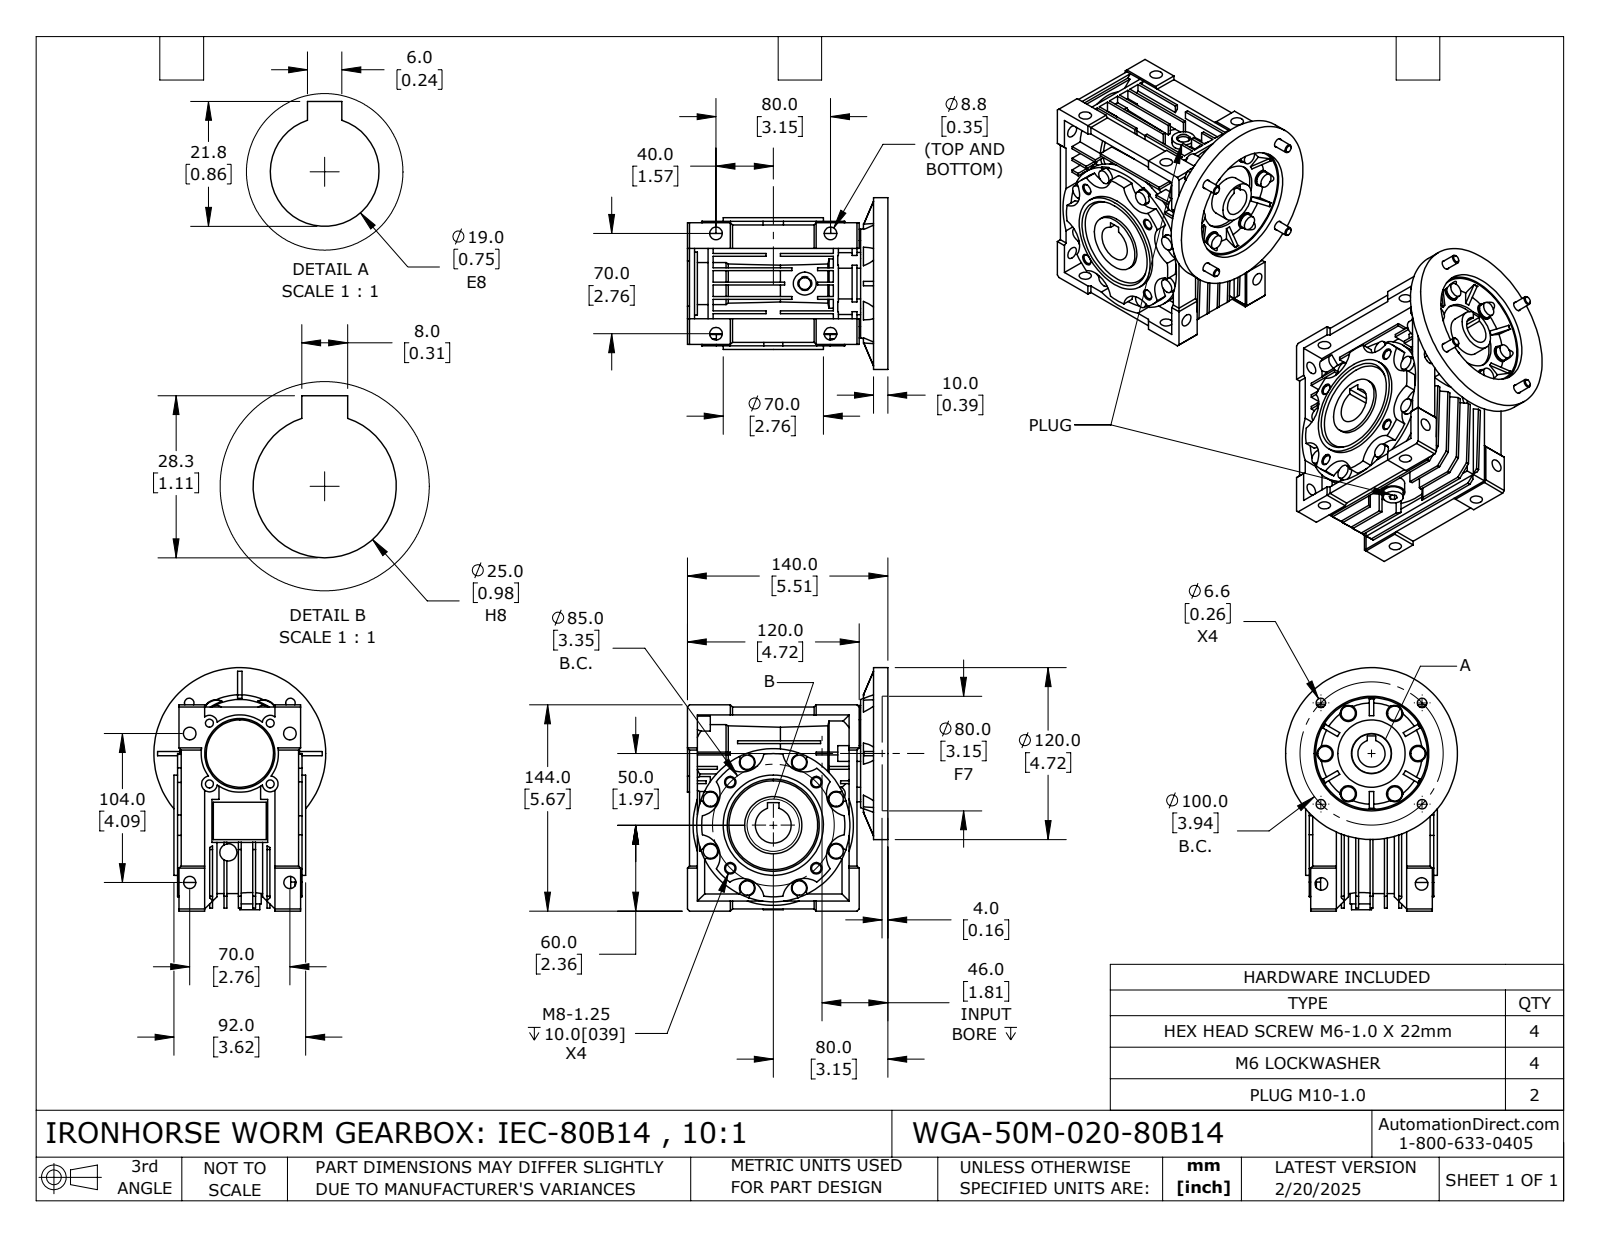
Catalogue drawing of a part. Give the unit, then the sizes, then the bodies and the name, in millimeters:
Units: millimetres
Overall size (bounding box): 170 × 150.5 × 120
Round holes (diameter × count): ⌀8.8 ×8, ⌀8.5 ×6, ⌀5.55 ×4, ⌀6.1 ×4, ⌀6.6 ×4, ⌀6.65 ×2, ⌀6.65 ×2, ⌀9 ×2, ⌀19 ×1, ⌀20 ×1, ⌀25 ×1, ⌀28 ×1
Round bosses / shafts (diameter × count): ⌀10 ×14, ⌀12.2 ×4, ⌀6 ×4, ⌀16 ×2, ⌀120 ×1, ⌀107 ×1, ⌀70 ×1, ⌀61 ×1
Partial cylindrical surfaces — rounded edges, fillets, slot ends (radius × count): R5.5 ×18, R6 ×8, R15 ×8, R15.5 ×8, R5.75 ×6, R20.76 ×1, R46 ×1, R47.7 ×1
Main face-to-face distances: 10, 2, 7, 1.5, 8, 5.5, 20, 2.5, 55, 35
Hole centre spacings: 58.31, 80, 70, 20.01, 30, 42.42, 42.5, 50.01
Volume: 1 088 000 mm³ · Surface area: 242 203 mm²
Bodies: 14 solids, 1080 faces (600 planar, 339 cylindrical, 141 other)
Part name (STEP PRODUCT): WGA-50M-020-80B14
STEP written by: SolidWorks 2024 (CONFIG_CONTROL_DESIGN)
